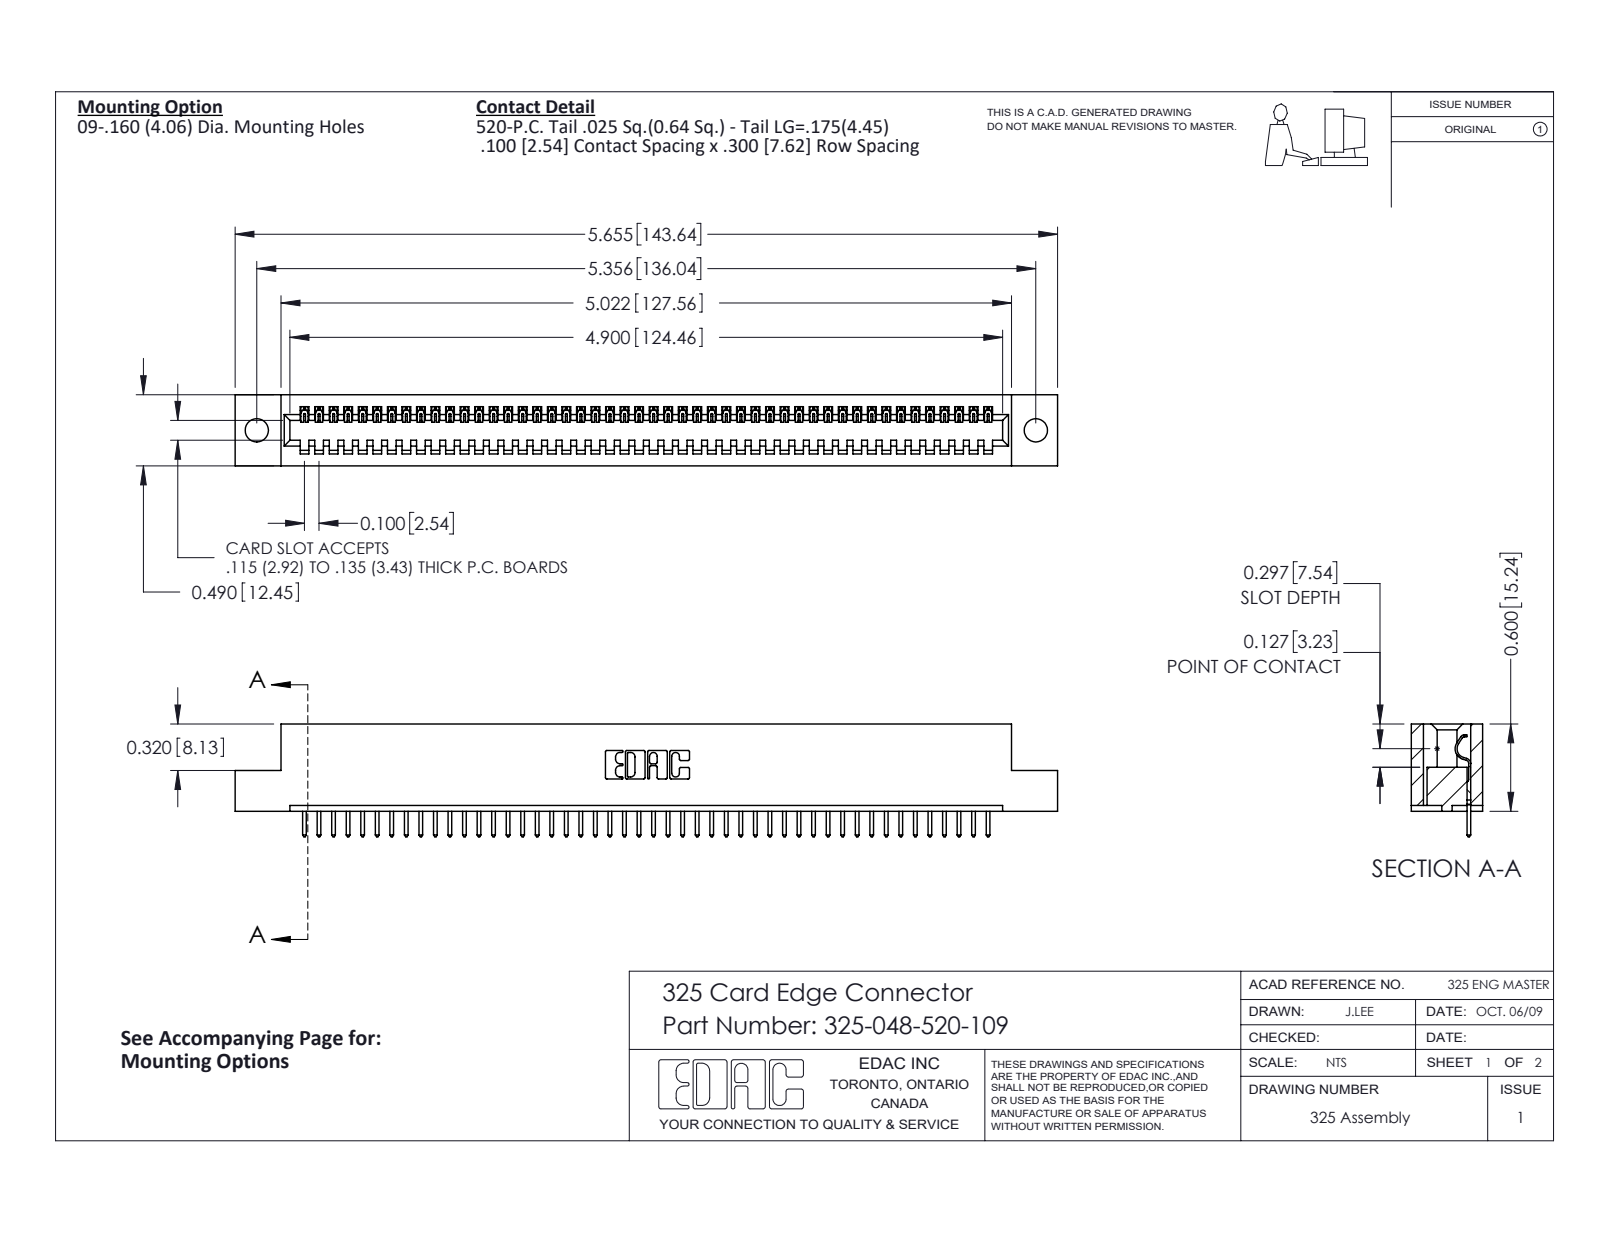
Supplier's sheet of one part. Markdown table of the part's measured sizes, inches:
| quantity | value |
| --- | --- |
| part name | 325-292-001_325-293-120; 325 Part_.160 TH; 325-048-520-109 |
| STEP written by | SolidWorks 2016 (CONFIG_CONTROL_DESIGN) |
| units | inches |
| bodies | 49 solids, 2898 faces (2086 planar, 812 cylindrical, 0 other) |
| overall size | 5.655 × 0.775 × 0.49 |
| volume | 1.094 in³ |
| surface area | 29.57 in² |
| round holes (diameter × count) | 0.16 × 2 |
| partial cylindrical surfaces (radius × count) | 0.006 × 96, 0.01 × 96, 0.01 × 22, 0.007 × 6, 0.031 × 6, 0.026 × 3, 0.014 × 1, 0.022 × 1 |
| main face-to-face distances | 0.083, 0.407, 0.49, 0.3, 0.107, 0.383, 0.025, 0.325, 0.56, 0.263 |
| hole center spacings | 5.356 |
